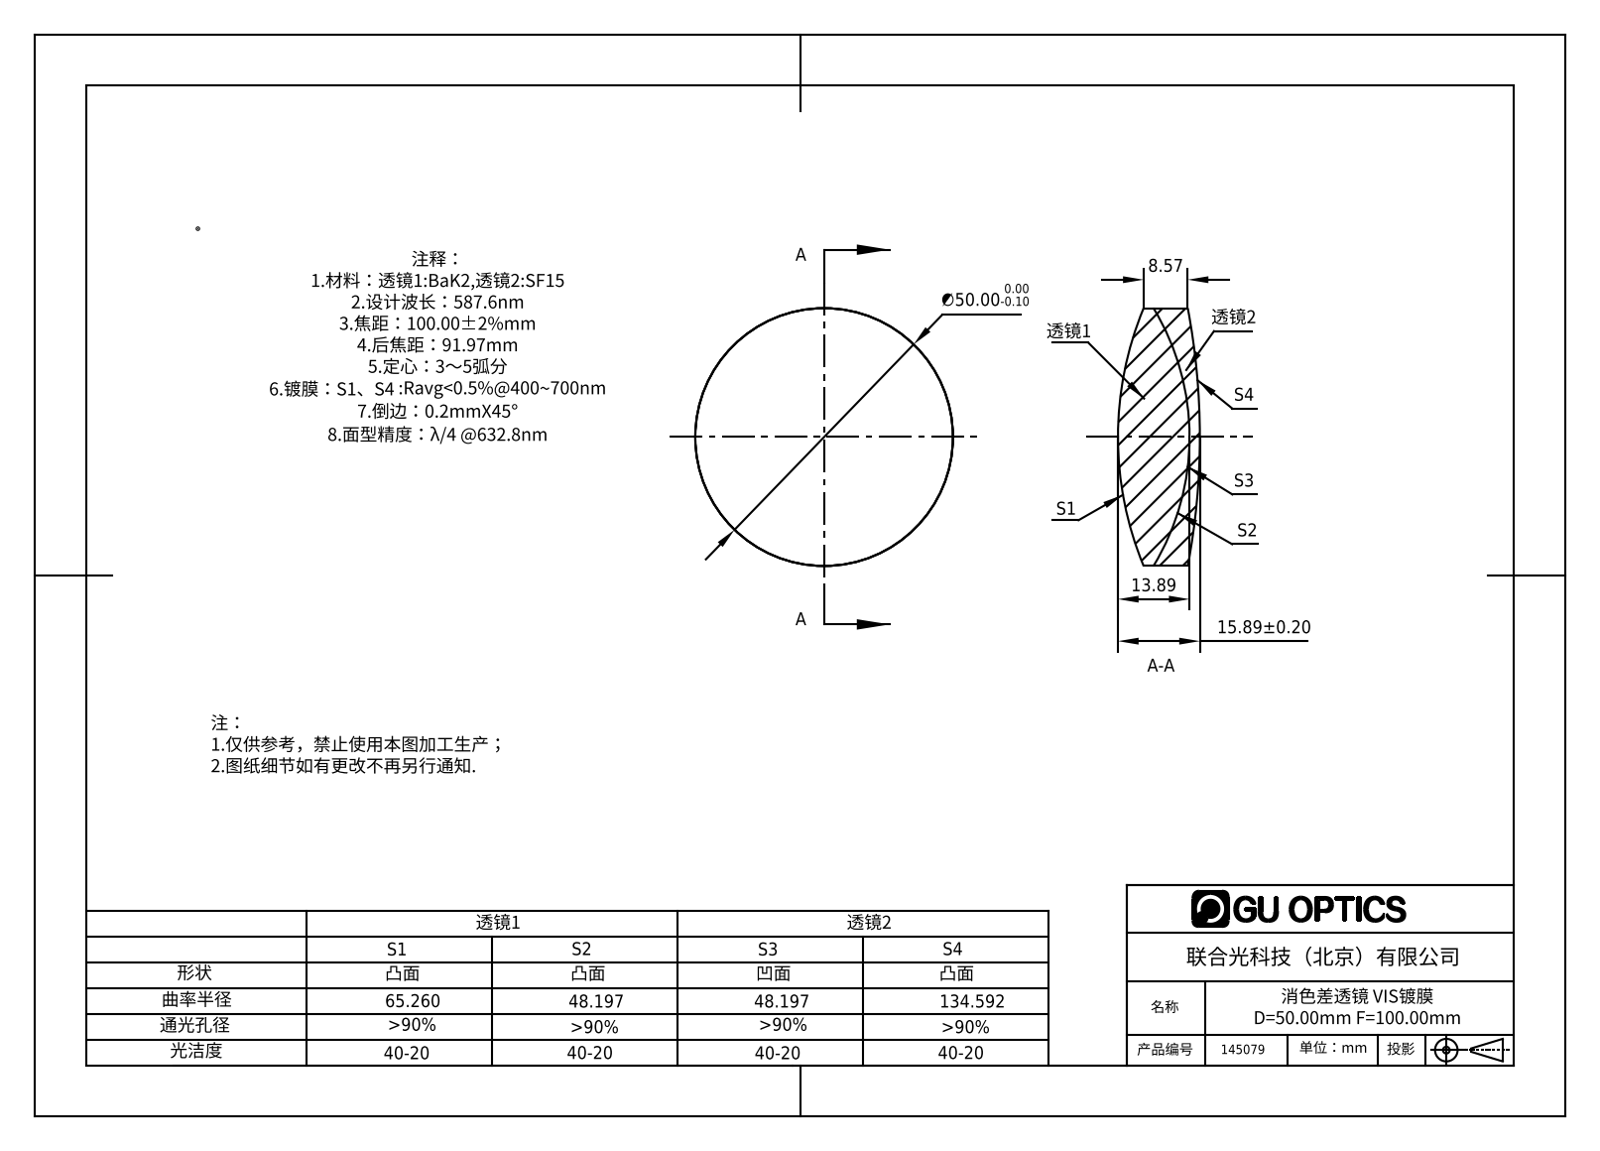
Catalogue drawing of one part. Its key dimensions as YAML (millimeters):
part_name: "145079"
step_written_by: "SolidWorks 2016 (AUTOMOTIVE_DESIGN)"
units: millimeters
bodies: {solids: 2, faces: 12, planar: 0, cylindrical: 4, other: 8}
overall_size: [50, 50, 15.89]
volume: 24084
surface_area: 9602
round_bosses_or_shafts:
  - {diameter: 50, count: 1}
